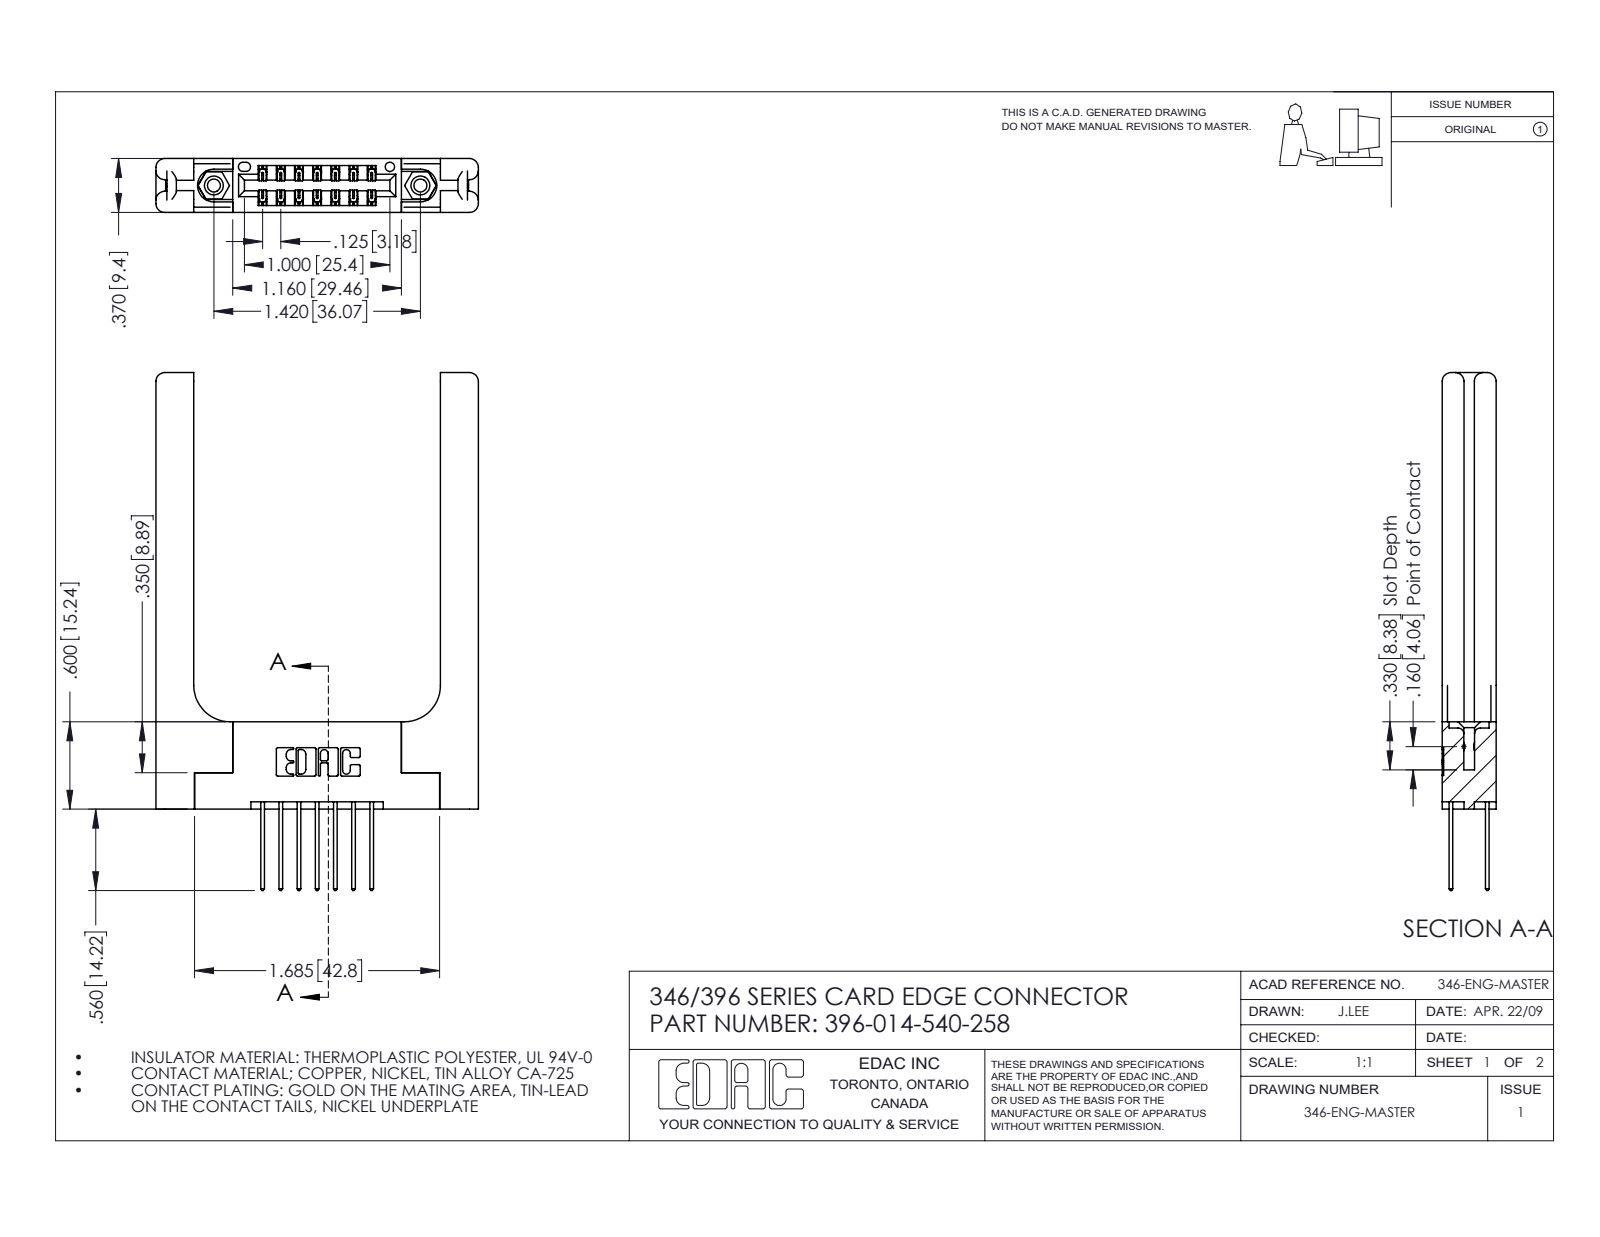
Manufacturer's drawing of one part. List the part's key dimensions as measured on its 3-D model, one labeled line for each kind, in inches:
Part name (STEP PRODUCT): 396-014-540-258; 345-250-001_345-250-001-102; 346-220-058_345-220-058; 346 Part_Flush Mounting Lugs - 0.156 Dia-TH (+1 more)
STEP written by: SolidWorks 2016 (CONFIG_CONTROL_DESIGN)
Units: inches
Bodies: 19 solids, 1106 faces (714 planar, 332 cylindrical, 60 other)
Overall size (bounding box): 3.56 × 2.216 × 0.37
Volume: 0.779 in³ · Surface area: 18.47 in²
Round holes (diameter × count): ⌀0.089 ×2, ⌀0.125 ×2, ⌀0.156 ×2, ⌀0.064 ×1
Round bosses / shafts (diameter × count): ⌀0.155 ×2
Partial cylindrical surfaces — rounded edges, fillets, slot ends (radius × count): R0.01 ×22, R0.006 ×21, R0.06 ×16, R0.01 ×14, R0.007 ×6, R0.031 ×6, R0.026 ×3, R0.014 ×2
Main face-to-face distances: 0.37, 0.15, 0.22, 0.072, 0.25, 0.148, 0.102, 0.048, 0.322, 0.173
Hole centre spacings: 0.246, 1.217, 1.42
